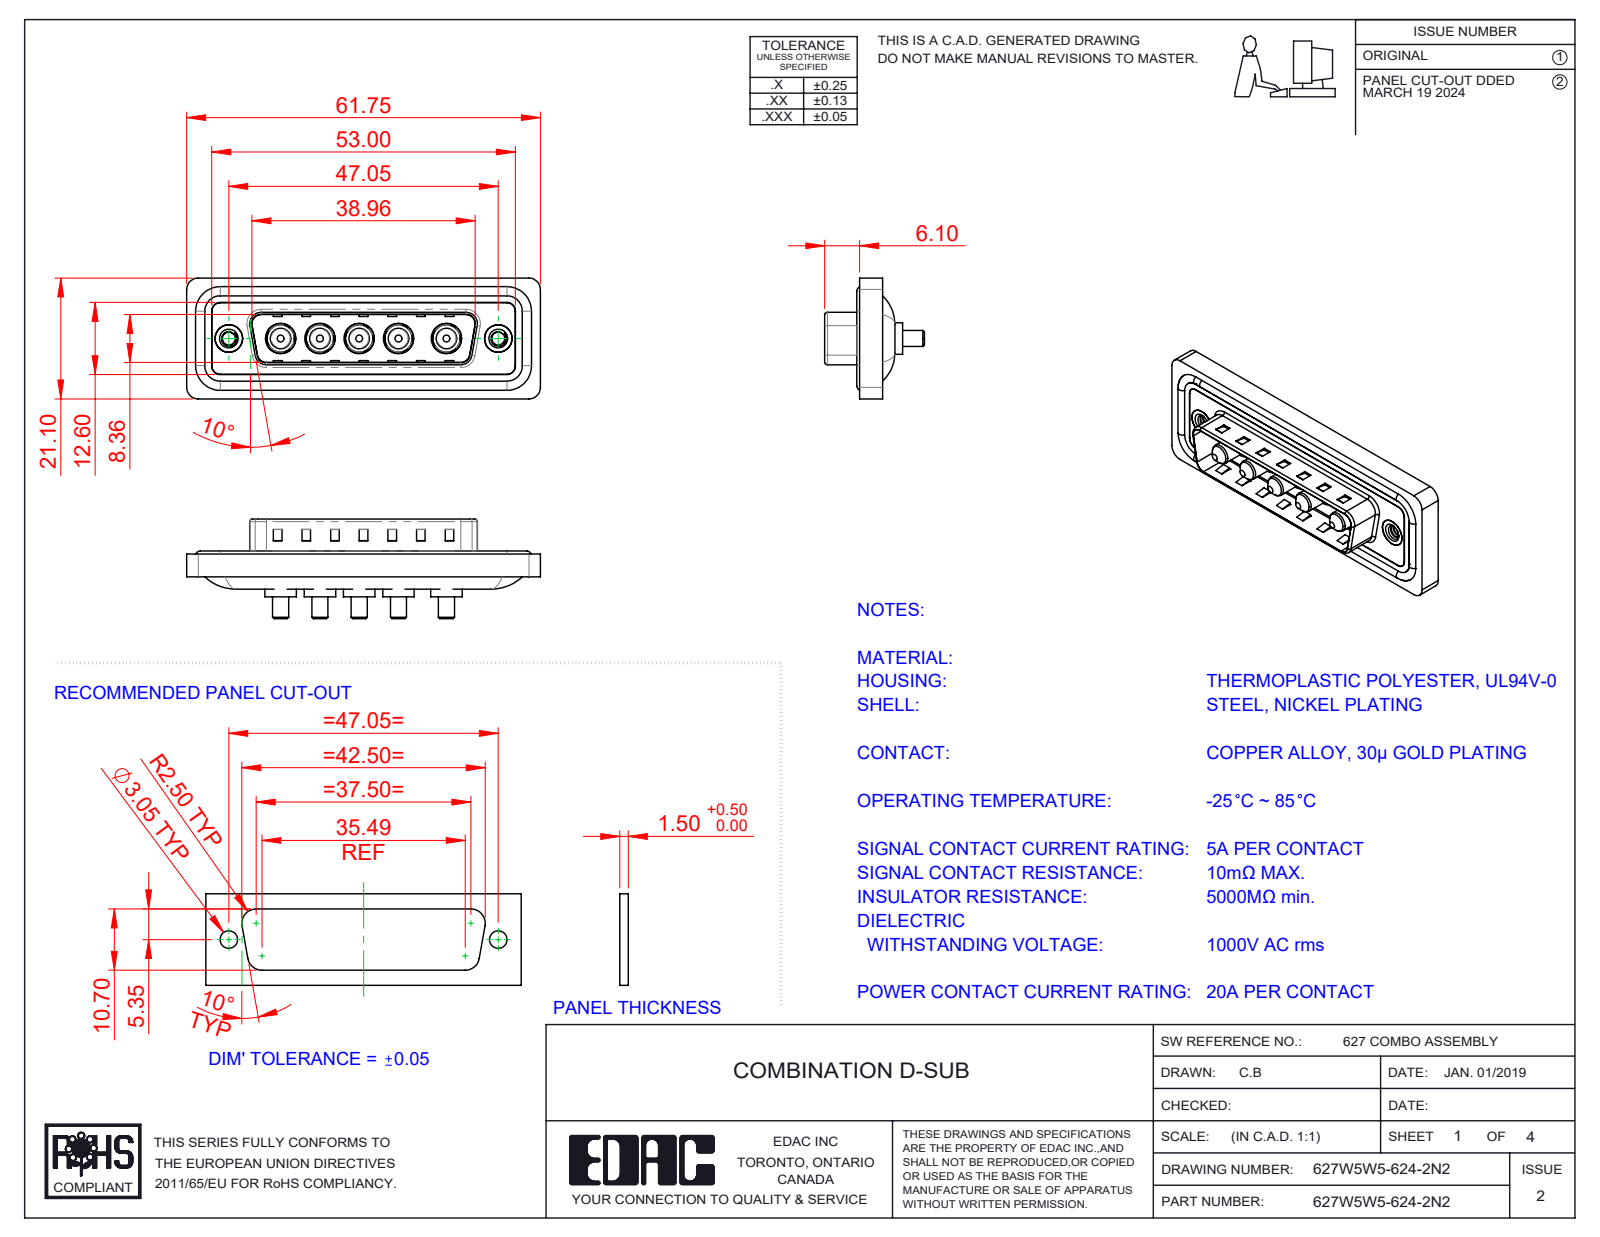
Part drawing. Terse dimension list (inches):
name: 627Combo Shell Front_25 Contacts; 627Combo Waterproof Housing_25 Contacts; 627Combo Shell Rear_25 Contacts; 627W5W5-624-2N2 (+3 more)
written by: SolidWorks 2023 (CONFIG_CONTROL_DESIGN)
unit: in
bodies: 17 solids, 678 faces (259 planar, 283 cylindrical, 136 other)
size: 2.431 × 0.831 × 0.685
volume: 0.456 in³; area: 18.28 in²
holes: 5× ⌀0.191, 5× ⌀0.209, 2× ⌀0.089, 2× ⌀0.157, 2× ⌀0.189, 2× ⌀0.197
bosses: 5× ⌀0.217, 5× ⌀0.205, 5× ⌀0.187, 5× ⌀0.148, 5× ⌀0.142, 5× ⌀0.11, 4× ⌀0.063, 2× ⌀0.193
rounds: 22× R0.059, 18× R0.079, 8× R0.02, 8× R0.063, 5× R0.083, 4× R0.01, 4× R0.024, 4× R0.026
face distances: 0.016, 0.059, 0.02, 0.043, 0.122, 0.063, 0.114, 0.032, 0.377, 0.222
hole spacings: 0.27, 0.356, 0.541, 1.496, 0.27, 0.33, 0.33, 0.356
